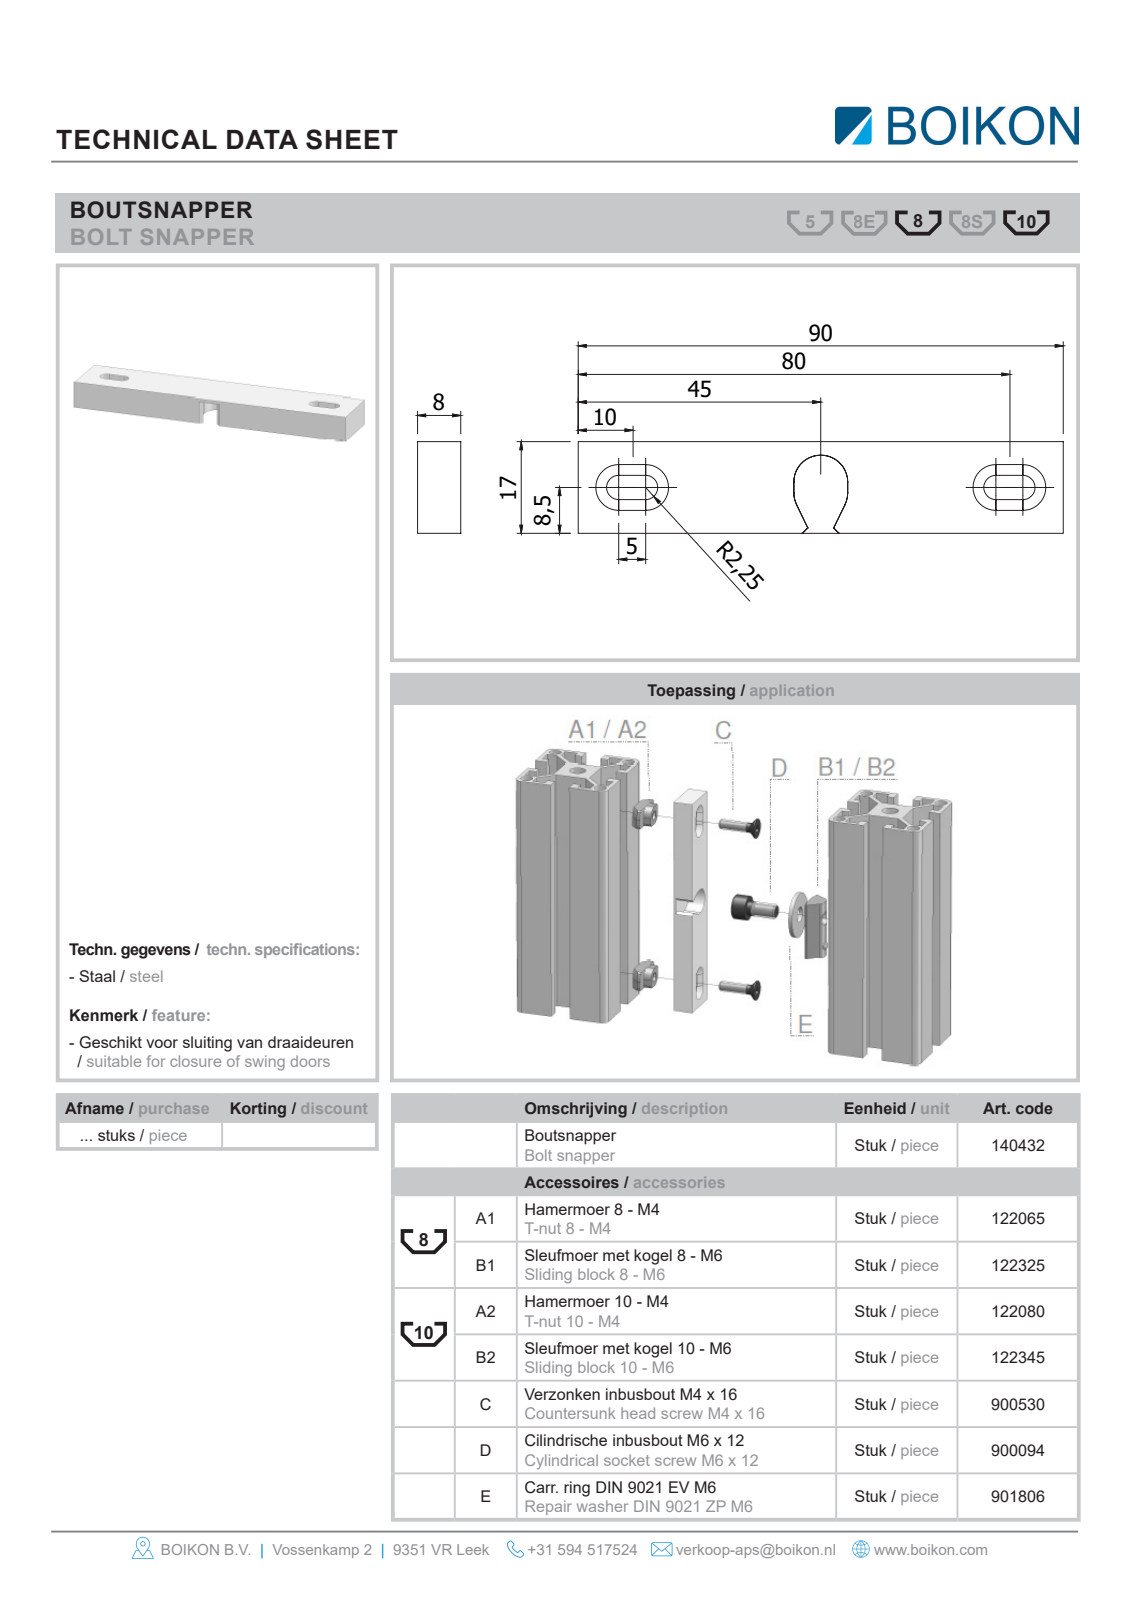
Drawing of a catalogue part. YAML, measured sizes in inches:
part_name: "Root; 140432BoutsnapperBOIKON; 900530Verz. inbusbout DIN 7991 EV M4 x 16BOIKON0; 900094Cil. inbusbout DIN 912 EV M6 x 12BOIKON0 (+1 more)"
step_written_by: "HiCAD 2013 1802.4 Build 509 (AUTOMOTIVE_DESIGN)"
units: inches
bodies: {solids: 5, faces: 85, planar: 56, cylindrical: 18, other: 11}
overall_size: [3.543, 1.157, 0.709]
volume: 0.736
surface_area: 10.63
round_holes:
  - {diameter: 0.252, count: 1}
round_bosses_or_shafts:
  - {diameter: 0.315, count: 2}
  - {diameter: 0.157, count: 2}
  - {diameter: 0.124, count: 2}
  - {diameter: 0.709, count: 1}
  - {diameter: 0.394, count: 1}
  - {diameter: 0.236, count: 1}
  - {diameter: 0.188, count: 1}
partial_cylinders:
  - {radius: 0.089, count: 4}
  - {radius: 0.197, count: 2}
face_to_face_distances: [0.315, 0.669, 0.37, 0.055, 0.433, 0.118, 0.063, 3.543, 0.394, 0.039]
